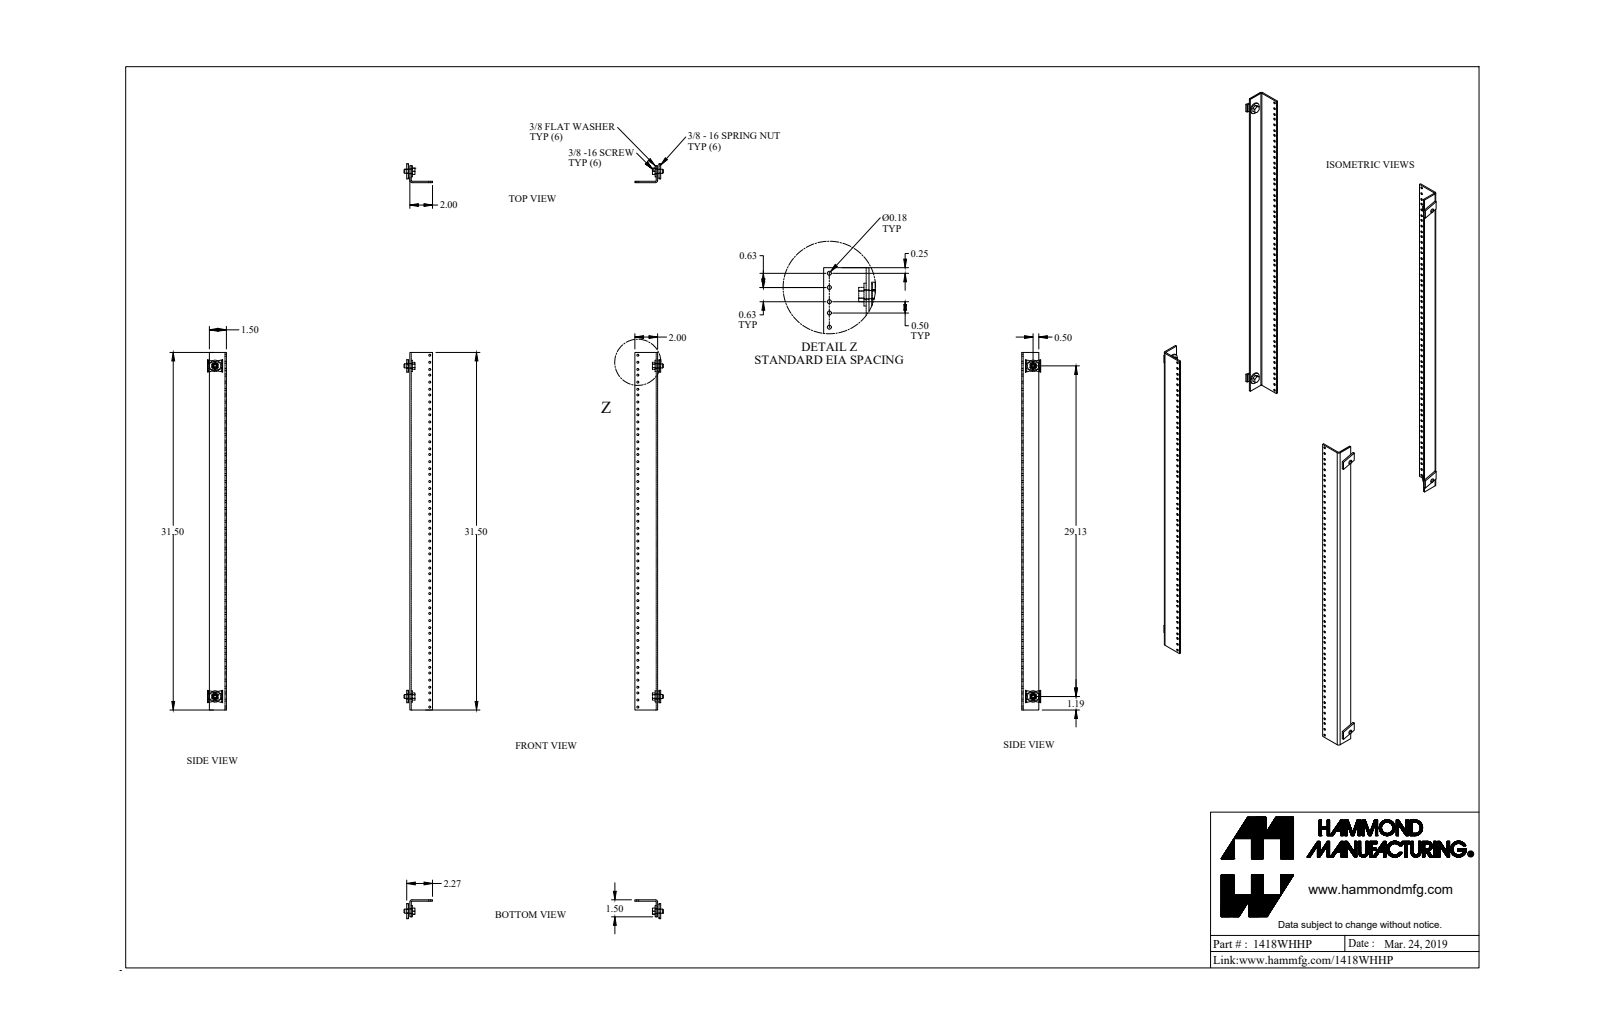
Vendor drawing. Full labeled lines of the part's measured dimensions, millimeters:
Part name (STEP PRODUCT): 1418WHHP_Default
STEP written by: SolidWorks 2019 (CONFIG_CONTROL_DESIGN)
Units: millimetres
Bodies: 14 solids, 392 faces (124 planar, 260 cylindrical, 8 other)
Overall size (bounding box): 800.1 × 580.5 × 42.4
Volume: 443 900 mm³ · Surface area: 298 400 mm²
Round holes (diameter × count): ⌀4.5 ×108, ⌀8 ×2, ⌀11.1 ×2, ⌀11.3 ×2
Round bosses / shafts (diameter × count): ⌀25.4 ×2, ⌀9.1 ×2
Partial cylindrical surfaces — rounded edges, fillets, slot ends (radius × count): R1.5 ×2, R4.7 ×2
Main face-to-face distances: 3.2, 3.2, 554.7, 548.4, 551.6, 551.6, 38.1, 34.9, 34.9, 50.8
Hole centre spacings: 44.5, 88.9, 133.4, 177.8, 222.3, 12.7, 31.8, 266.7
